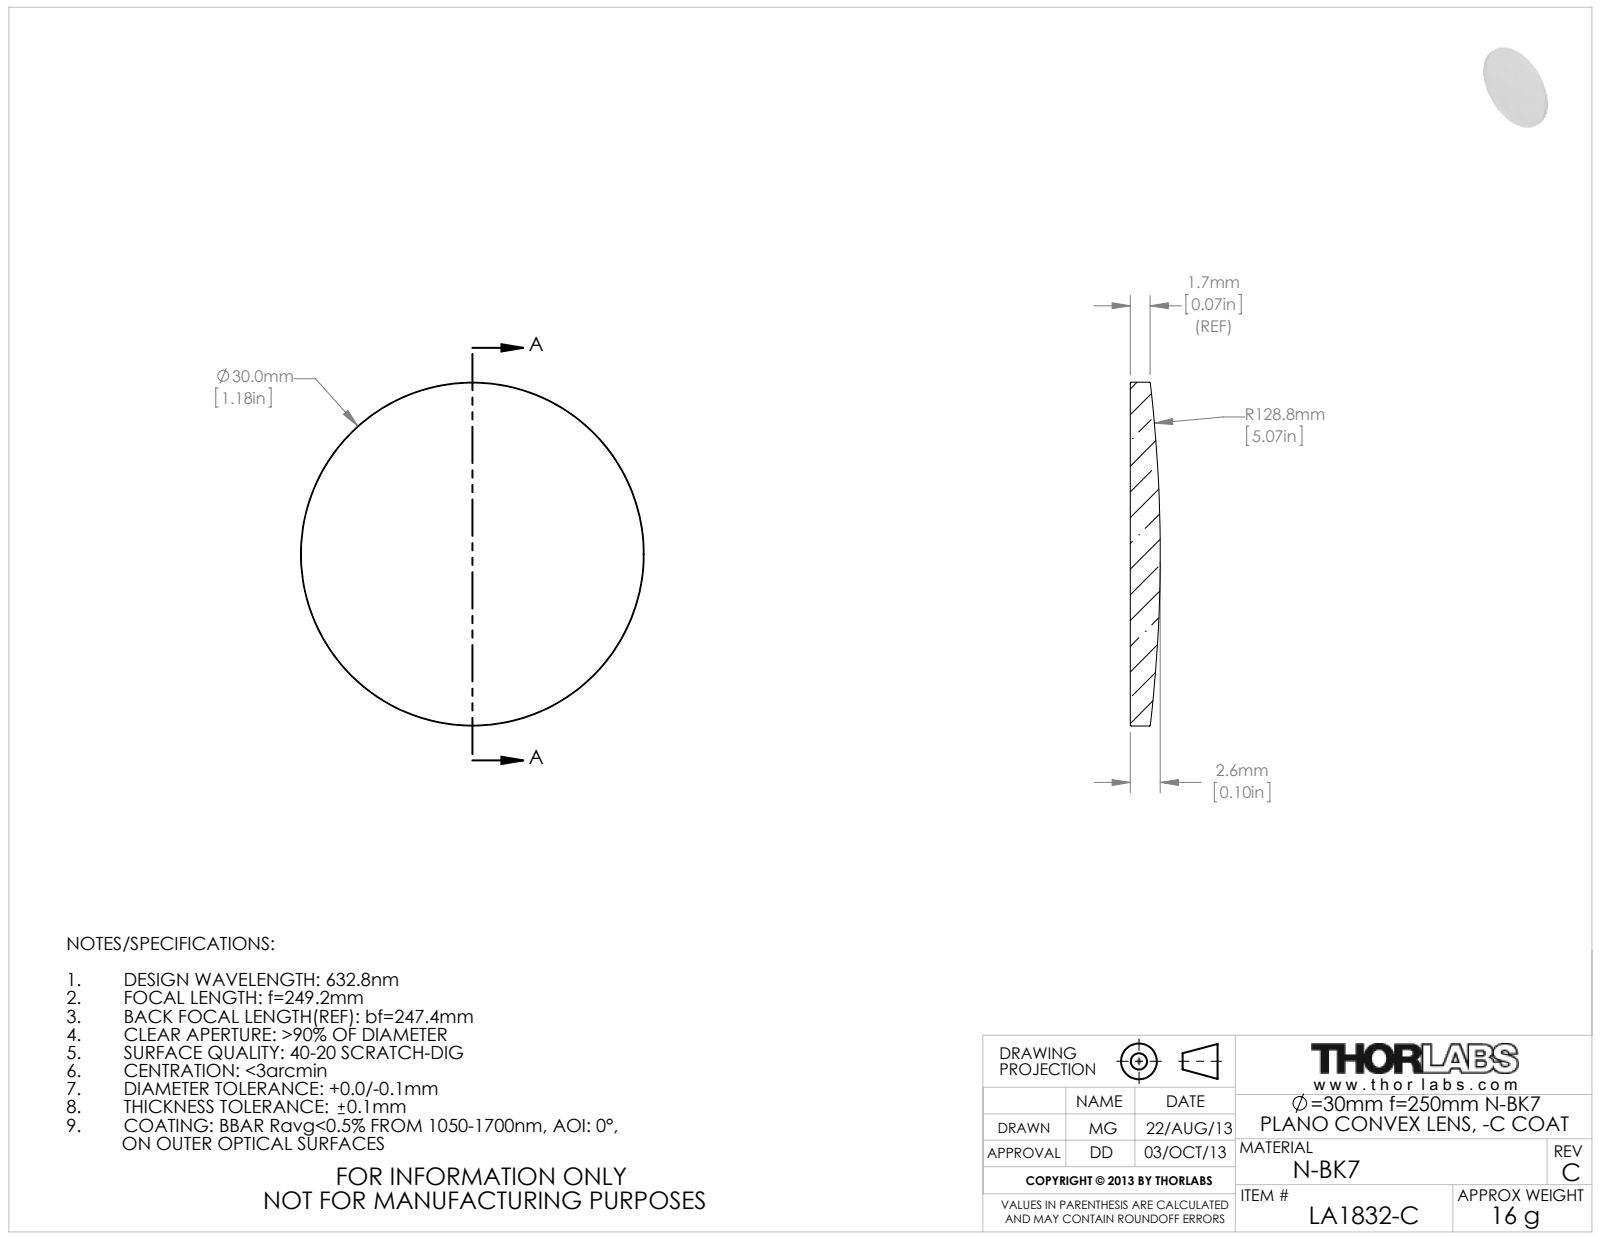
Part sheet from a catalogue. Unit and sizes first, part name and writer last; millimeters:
Units: millimetres
Overall size (bounding box): 30 × 30 × 2.62
Round bosses / shafts (diameter × count): ⌀30 ×1
Volume: 1 542 mm³ · Surface area: 1 580 mm²
Bodies: 1 solid, 5 faces (1 planar, 2 cylindrical, 2 other)
Part name (STEP PRODUCT): 19316-E0W
STEP written by: SolidWorks 2009 (AUTOMOTIVE_DESIGN)
